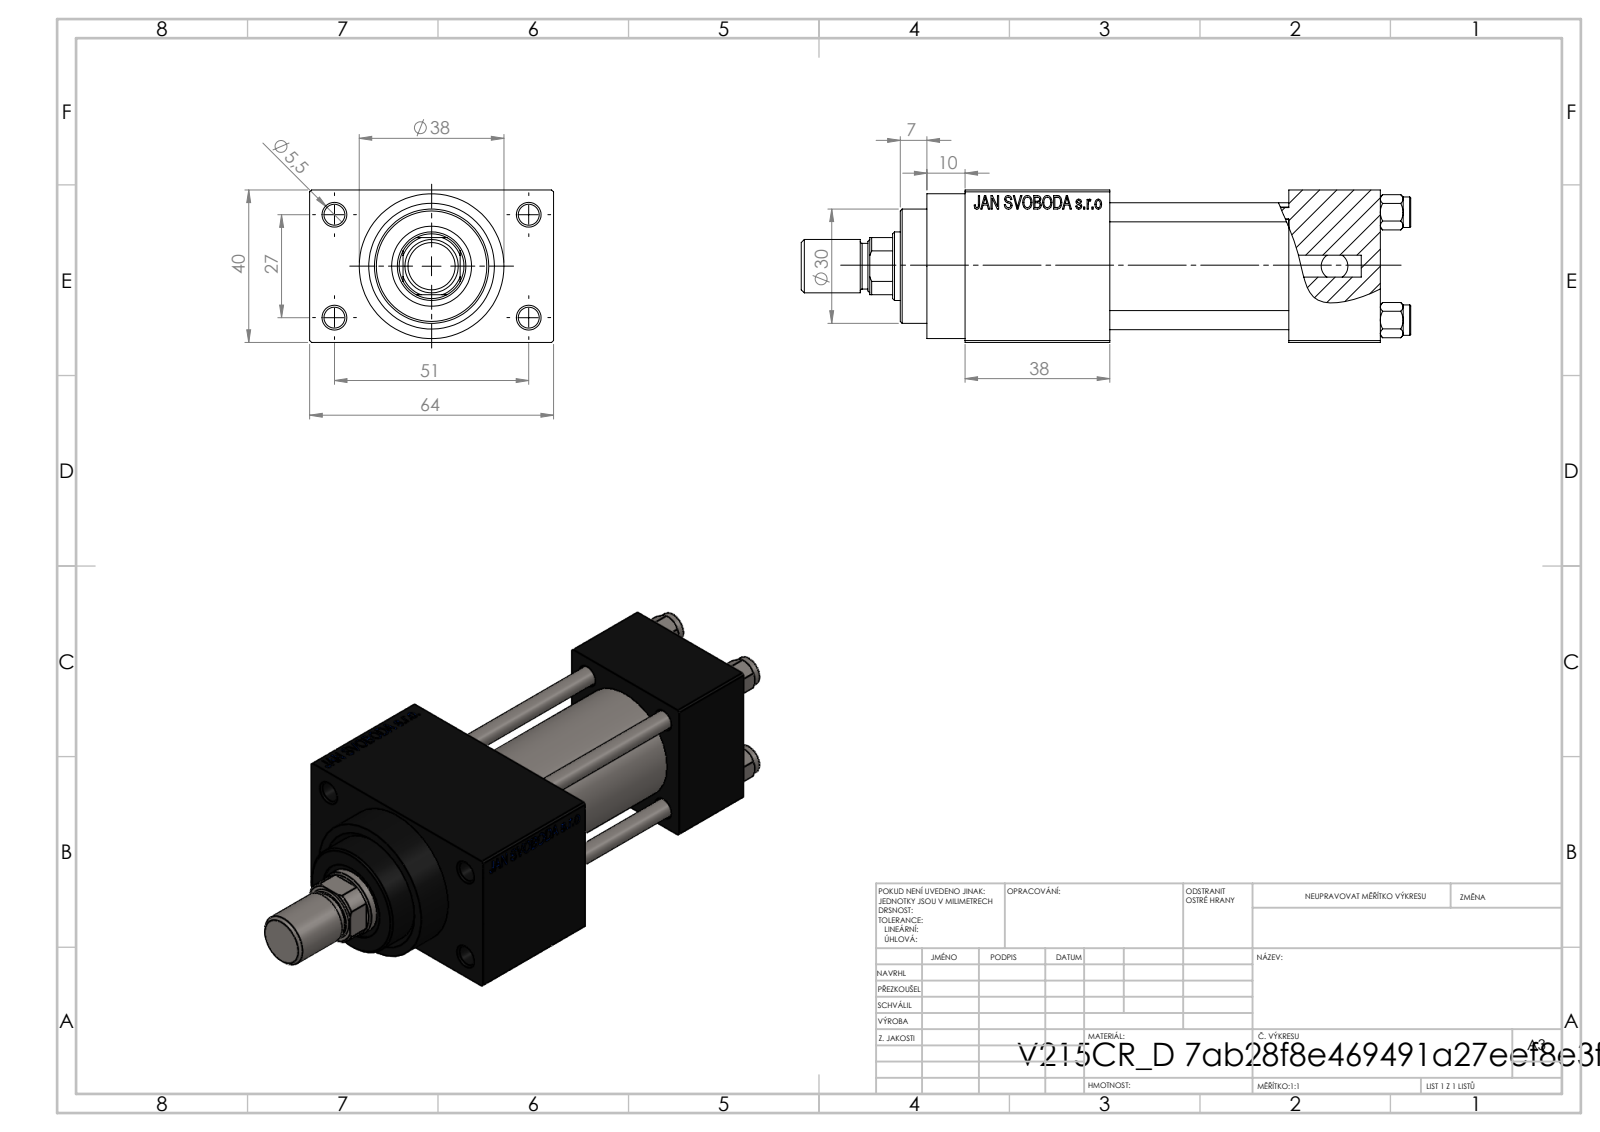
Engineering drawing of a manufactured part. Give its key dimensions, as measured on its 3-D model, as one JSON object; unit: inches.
{"part_name": "NUT_M5_D; V215CR_D_TYCINKA; ROD_END_AH; V215_VC_A (+2 more)", "step_written_by": "SolidWorks 2019 (CONFIG_CONTROL_DESIGN)", "units": "inches", "bodies": {"solids": 12, "faces": 1115, "planar": 499, "cylindrical": 90, "other": 526}, "overall_size": [6.299, 2.52, 1.575], "volume_in3": 11.09, "surface_area_in2": 101.9, "round_holes": [[0.197, 4], [0.217, 4], [0.787, 3], [0.276, 2], [0.518, 2], [0.335, 1], [0.709, 1], [0.827, 1], [0.984, 1], [1.181, 1]], "round_bosses_or_shafts": [[0.315, 4], [1.496, 1], [1.22, 1], [0.551, 1], [0.472, 1]], "partial_cylinders_radius": [[0.335, 1]], "face_to_face_distances": [1.575, 0.472, 1.85, 0.945, 2.795, 2.047, 1.496, 4.291, 3.346, 2.52], "hole_center_spacings": [0.448, 0.788, 1.114, 1.136, 1.177, 1.561, 1.903, 1.063]}
